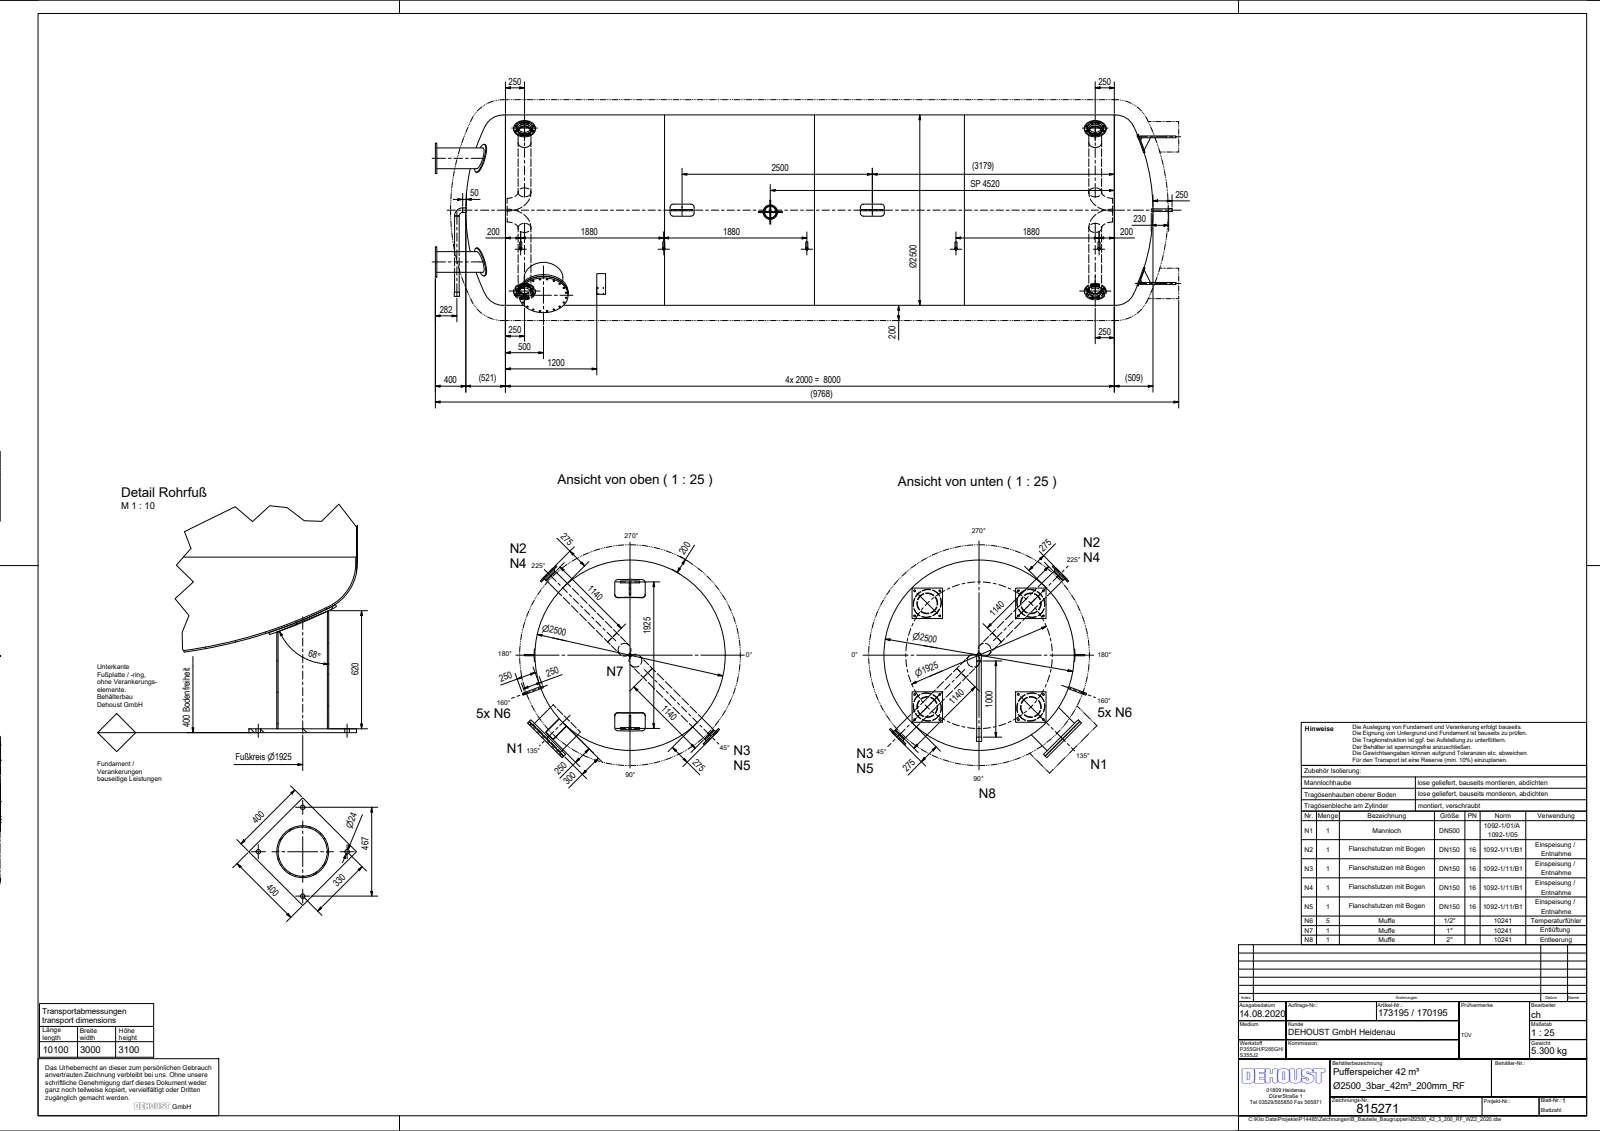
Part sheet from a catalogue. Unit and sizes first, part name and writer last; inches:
Units: inches
Overall size (bounding box): 383.153 × 104.884 × 102.204
Round holes (diameter × count): ⌀0.866 ×72, ⌀0.945 ×16, ⌀6.272 ×8, ⌀0.733 ×5, ⌀0.854 ×5, ⌀1.059 ×5, ⌀0.228 ×4, ⌀6.626 ×4, ⌀10.189 ×4, ⌀0.197 ×2, ⌀2.059 ×2, ⌀20 ×2
Round bosses / shafts (diameter × count): ⌀6.626 ×8, ⌀1.059 ×5, ⌀1.039 ×5, ⌀14.961 ×4, ⌀11.22 ×4, ⌀10.748 ×4, ⌀8.346 ×4, ⌀25.394 ×2
Partial cylindrical surfaces — rounded edges, fillets, slot ends (radius × count): R1.654 ×16, R0.236 ×8, R0.197 ×2, R0.394 ×2, R1.417 ×2, R2.835 ×2, R4.921 ×1, R49.567 ×1
Main face-to-face distances: 0.787, 23.622, 186.967, 205.274, 186.18, 204.487, 18.307, 1.102, 0.984, 25.591
Hole centre spacings: 11.811, 4.724, 4.725, 3.695, 7.3, 13.885, 295.276, 19.111
Volume: 39 330 in³ · Surface area: 263 300 in²
Bodies: 58 solids, 449 faces (178 planar, 225 cylindrical, 46 other)
Part name (STEP PRODUCT): Ø2500_42_3_200_RF_WZ2_2020; Klöpper_Gew_Ø2500_5,5; Klöpper_Gew_Ø2500_8,3; Zyl_Ø2500_5x8000_2020 (+8 more)
STEP written by: Autodesk Inventor 2019 (AUTOMOTIVE_DESIGN)
